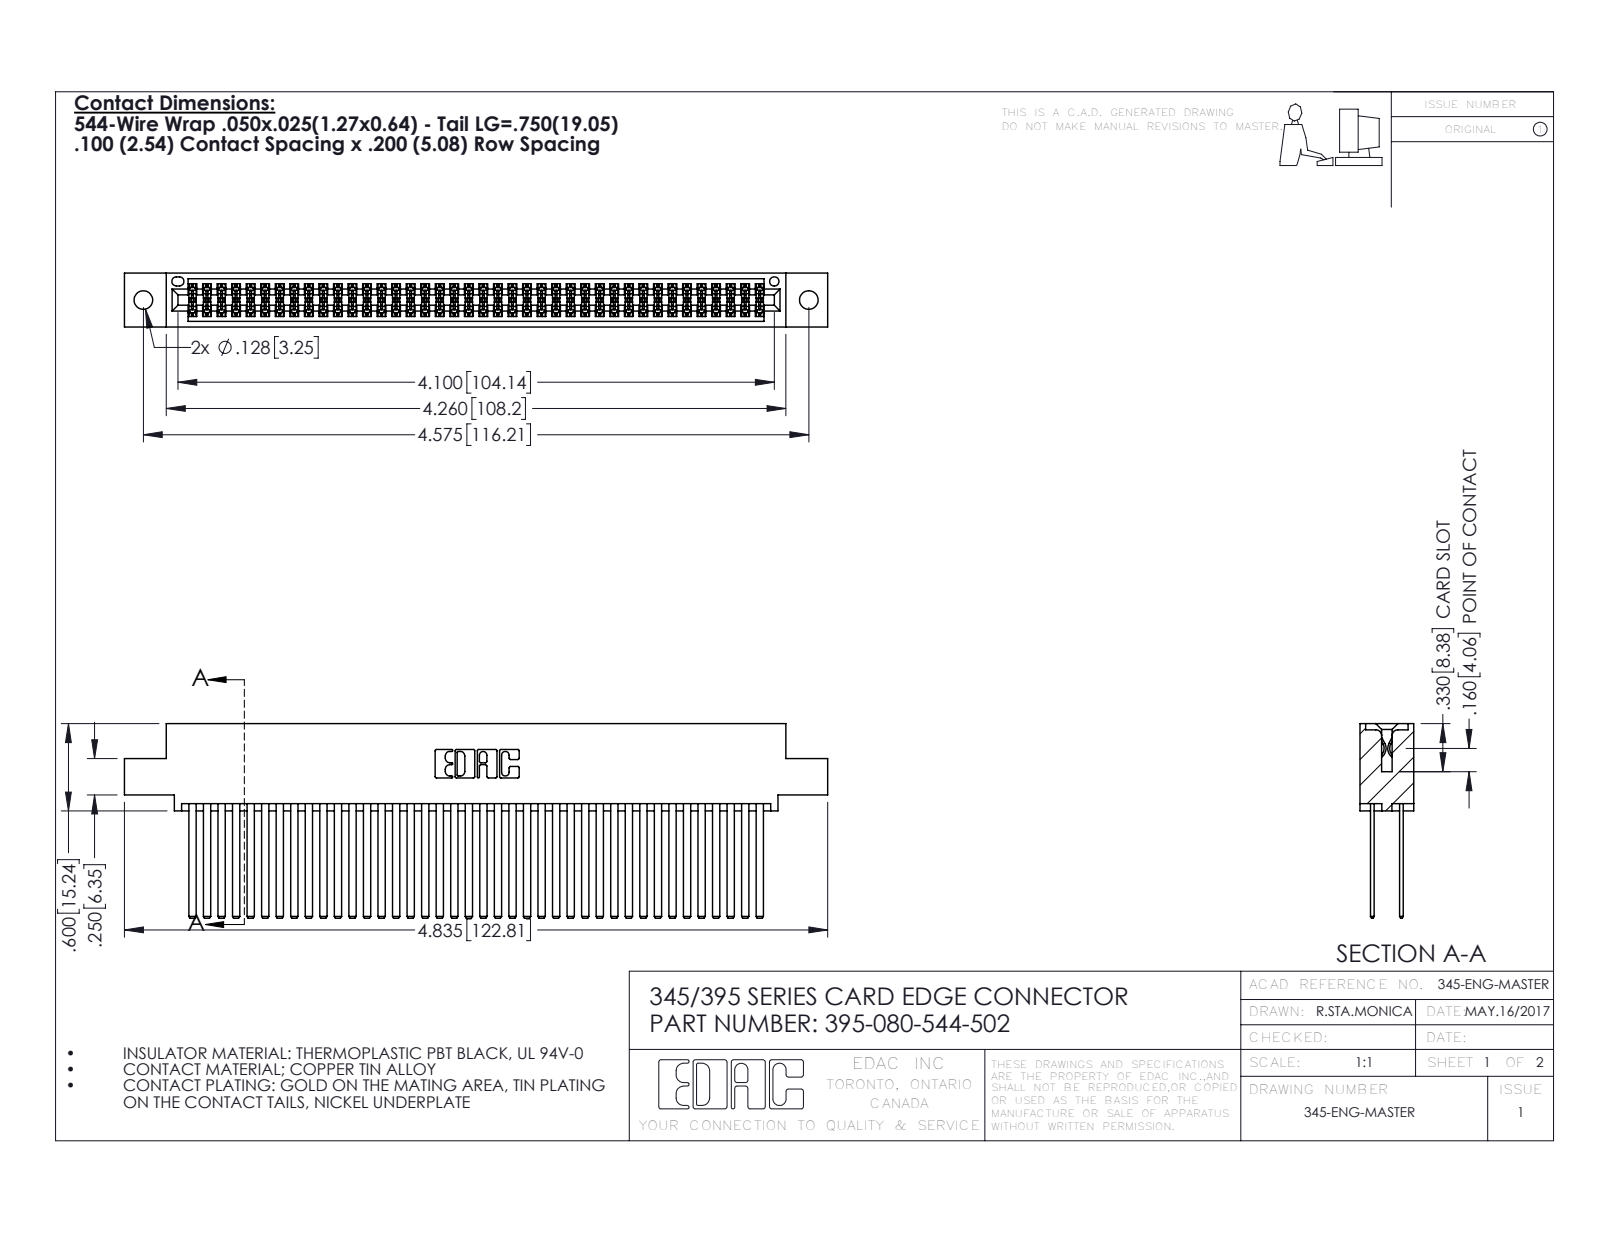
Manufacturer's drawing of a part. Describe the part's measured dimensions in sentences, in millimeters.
The part is named "395-080-544-502; 345 Part_0.110 Offset - 0.128 Dia; 345-292-001_345-293-144". Its 3-D file was written by "SolidWorks 2016 (CONFIG_CONTROL_DESIGN)". It is 81 solids with 3650 faces: 2404 planar, 1246 cylindrical and 0 other. Overall it measures 122.8 by 34 by 9.4 millimeters. Its volume is 12 900 cubic millimeters and its surface area 22 170 square millimeters. Round holes: 2 of diameter 3.3, 1 of diameter 1.6. Partial cylindrical surfaces (rounded edges, fillets, slot ends): 120 of radius 0.2, 22 of radius 0.3, 6 of radius 0.2, 6 of radius 0.8, 3 of radius 0.7, 2 of radius 0.4, 2 of radius 0.5, 2 of radius 0.6. The main face-to-face distances are 5.1, 0.6, 1.8, 2.5, 6.9, 7.6, 5.7, 4.4, 9.4, 1.3. The hole center spacings are 6.9, 110.2, 116.2.
